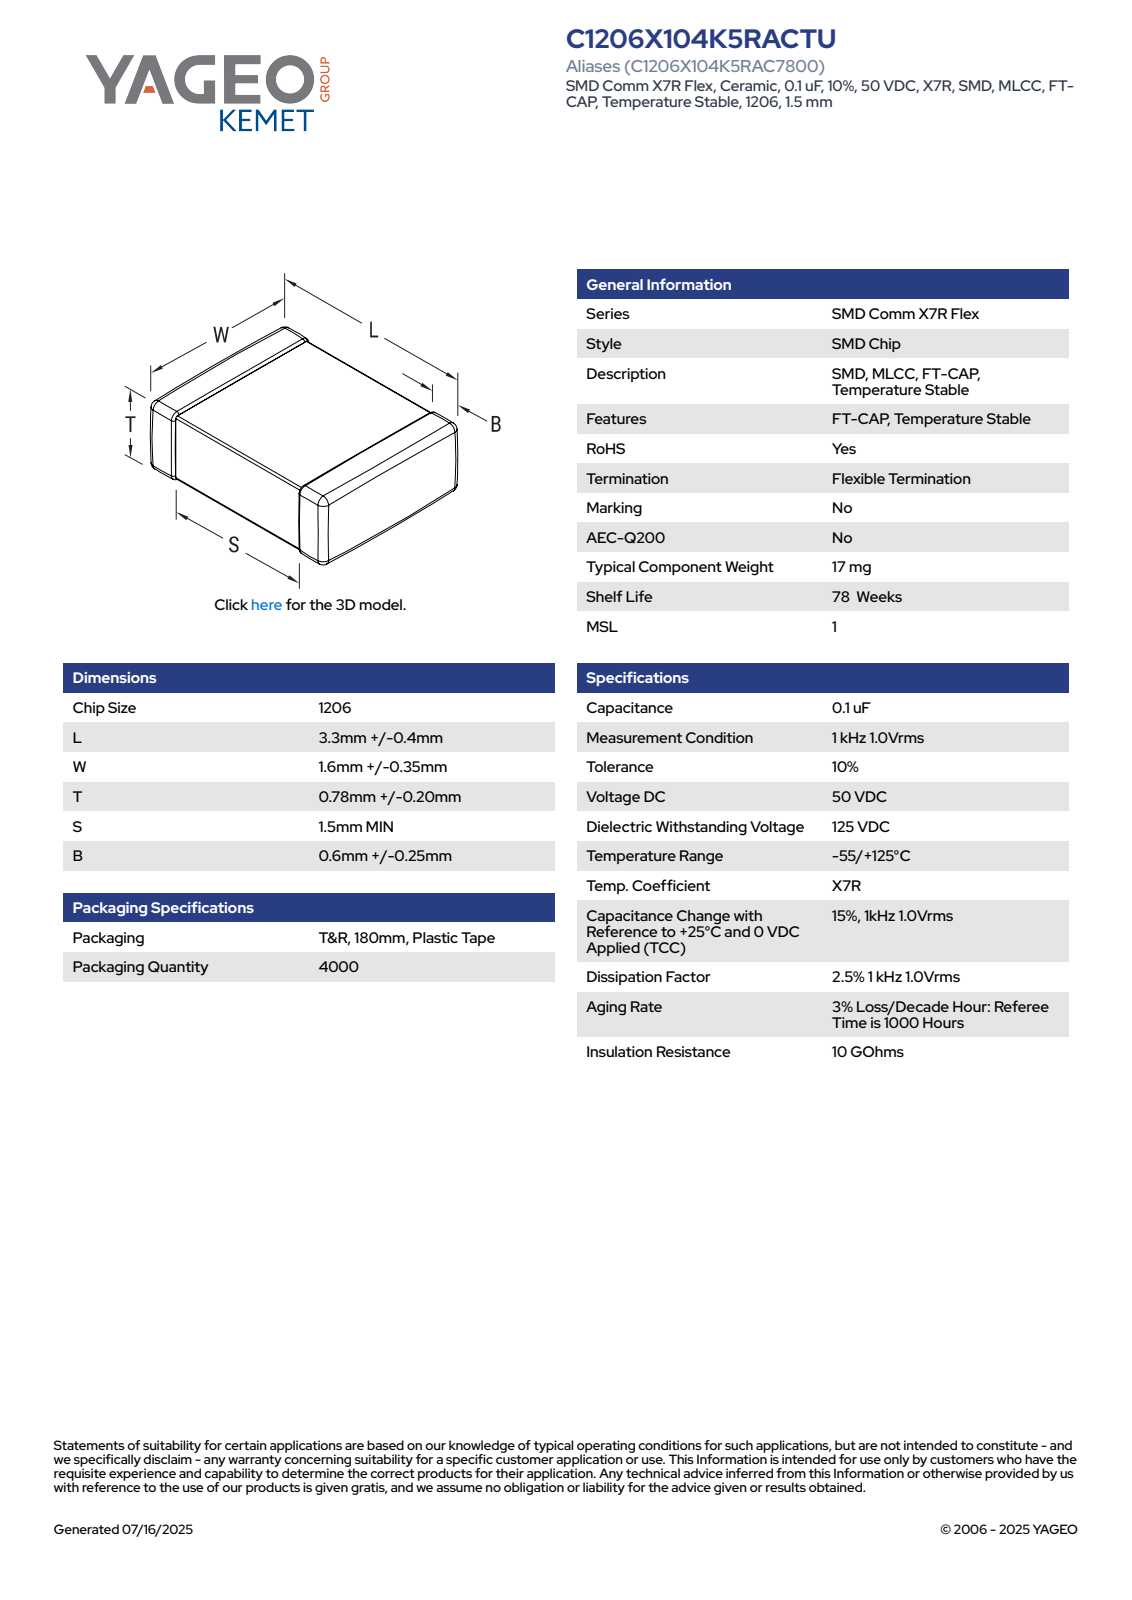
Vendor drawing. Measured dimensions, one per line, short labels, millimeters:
name: CCS_CCSTDNOS_1206_L3.7W1.95T0.98B0.85
written by: SolidWorks 2014 (AUTOMOTIVE_DESIGN)
unit: mm
bodies: 4 solids, 125 faces (71 planar, 38 cylindrical, 16 other)
size: 3.7 × 1.95 × 0.98
volume: 7 mm³; area: 25 mm²
face distances: 0.94, 0.9, 0.98, 1.91, 3.7, 1.87, 1.95, 0.86, 0.82, 1.05
